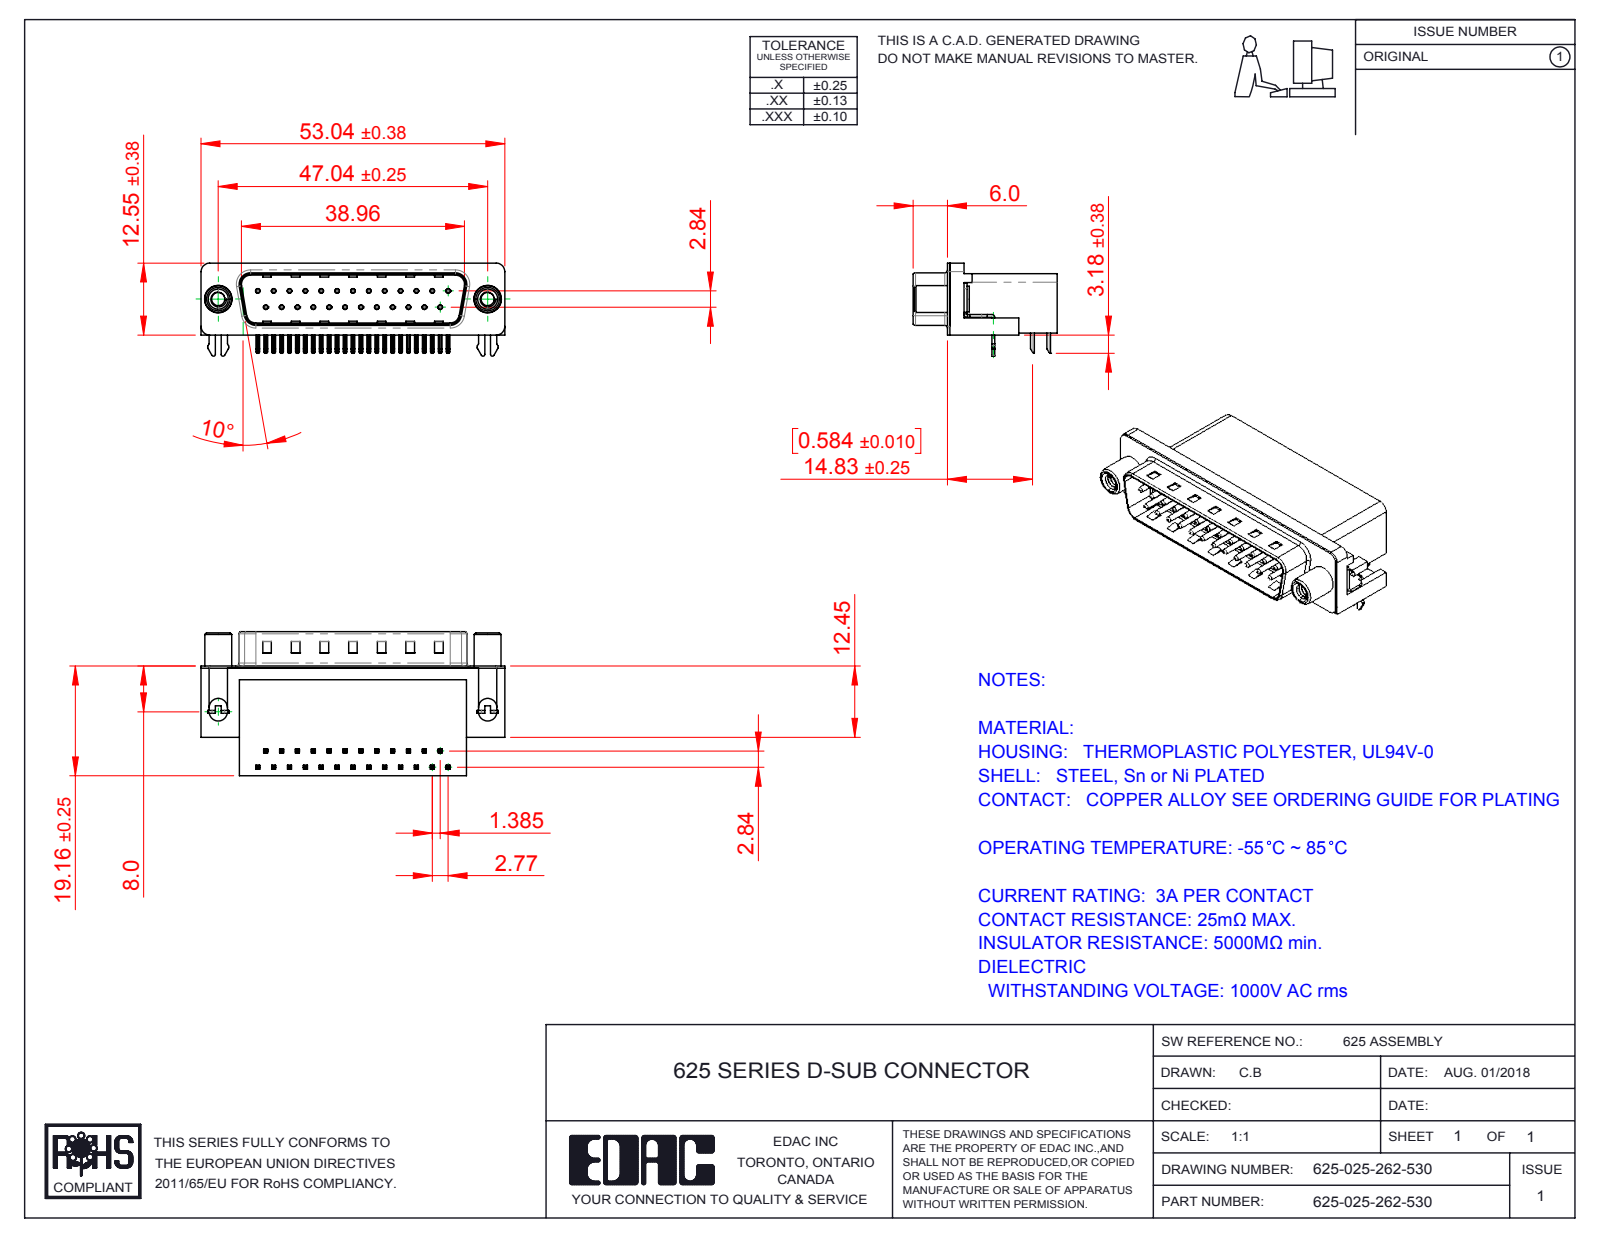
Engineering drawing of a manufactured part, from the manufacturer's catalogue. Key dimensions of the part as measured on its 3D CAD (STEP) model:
Part name (STEP PRODUCT): 625-025-262-530; 625 Contact Top; 625 Housing_25 Socket; 625 Shell_25 Socket (+3 more)
STEP written by: SolidWorks 2016 (CONFIG_CONTROL_DESIGN)
Units: millimetres
Bodies: 31 solids, 2299 faces (1429 planar, 677 cylindrical, 193 other)
Overall size (bounding box): 53.04 × 25.16 × 16.25
Volume: 9 254 mm³ · Surface area: 9 067 mm²
Round holes (diameter × count): ⌀0.35 ×25, ⌀0.8 ×25, ⌀2.3 ×2, ⌀3.1 ×2, ⌀4 ×2, ⌀4.8 ×2, ⌀5 ×2
Round bosses / shafts (diameter × count): ⌀0.75 ×25, ⌀4.9 ×2, ⌀4.7 ×2, ⌀4.5 ×2, ⌀3.85 ×2
Partial cylindrical surfaces — rounded edges, fillets, slot ends (radius × count): R0.25 ×100, R0.12 ×50, R1 ×16, R0.5 ×14, R1.6 ×8, R1.5 ×7, R0.32 ×4, R0.9 ×4
Main face-to-face distances: 0.4, 10.35, 18.76, 2.1, 8.76, 10.46, 10.86, 1.7, 19.16, 0.35
Hole centre spacings: 3.16, 2.77, 11.08, 5.54, 8.31, 5.03, 13.85, 7.48
